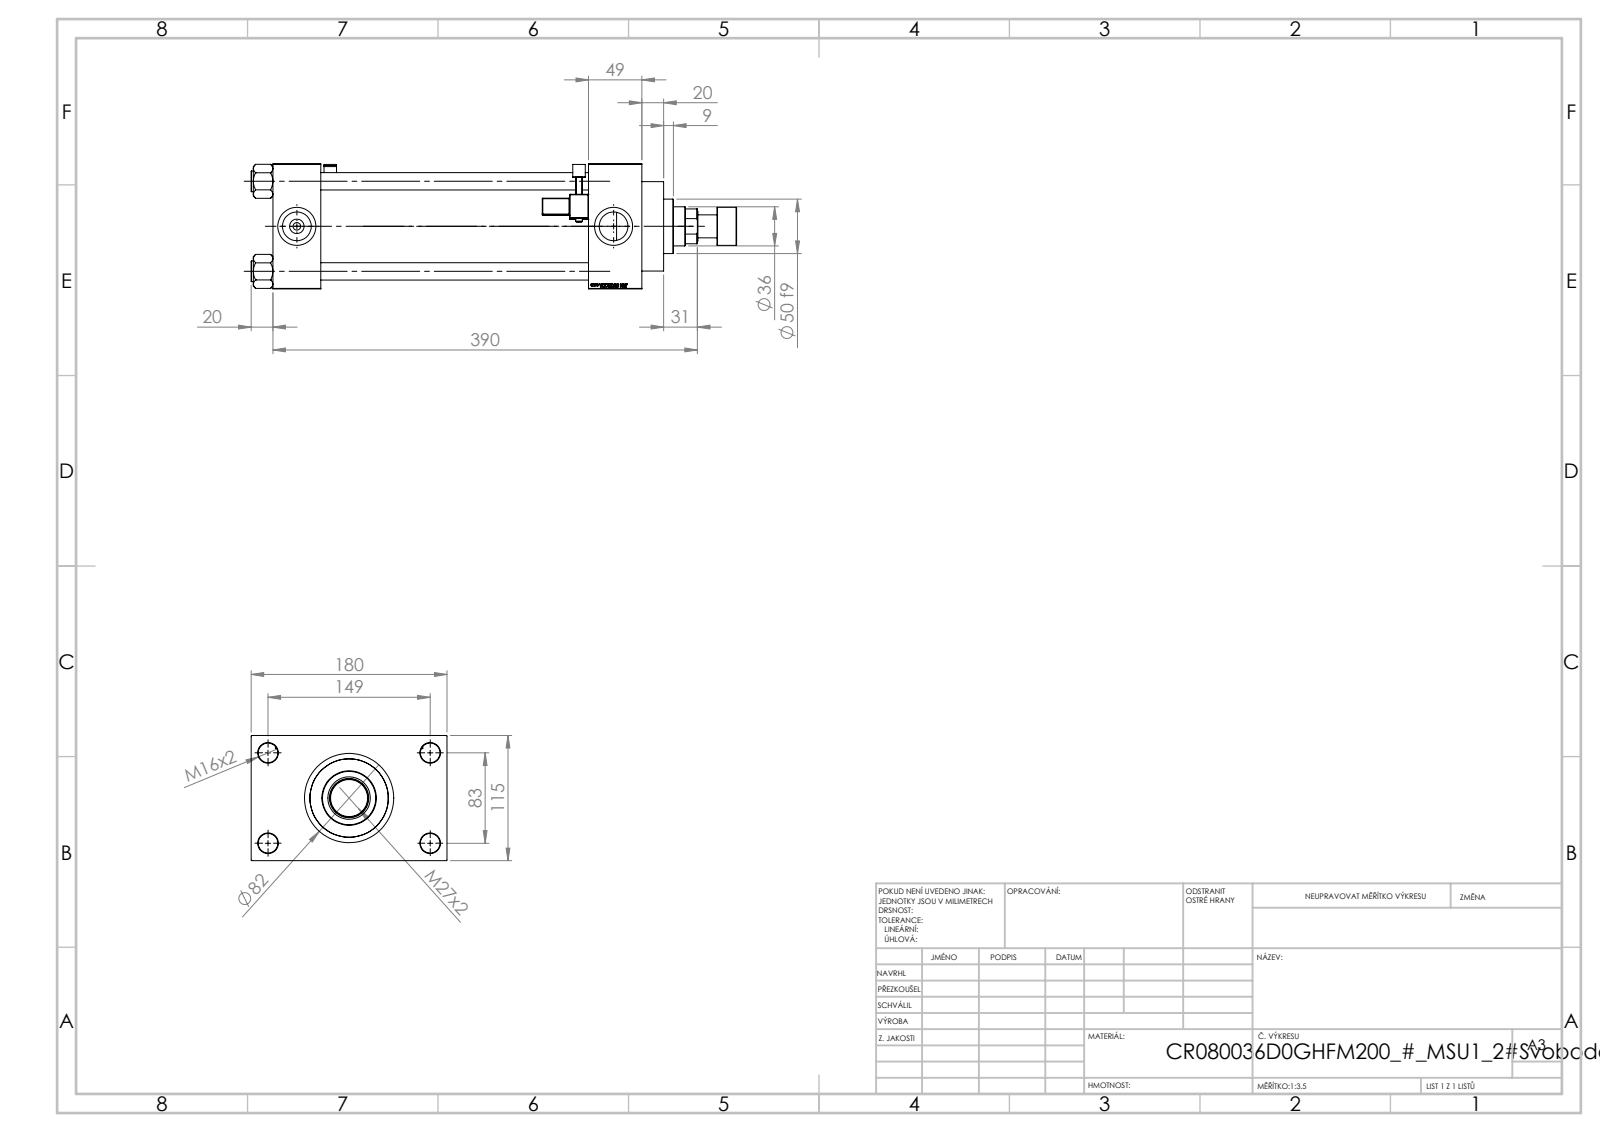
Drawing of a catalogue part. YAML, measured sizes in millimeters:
part_name: "V215CR_VCP_D; V215CR_D_TYCINKA; V215CR_ROD_END_F; V215_VC_A (+3 more)"
step_written_by: "SolidWorks 2019 (CONFIG_CONTROL_DESIGN)"
units: millimeters
bodies: {solids: 14, faces: 1319, planar: 607, cylindrical: 152, other: 560}
overall_size: [446, 180, 115]
volume: 2513000
surface_area: 465033
round_holes:
  - {diameter: 16, count: 4}
  - {diameter: 18, count: 4}
  - {diameter: 7, count: 2}
  - {diameter: 26.44, count: 2}
  - {diameter: 35, count: 2}
  - {diameter: 25.5, count: 1}
  - {diameter: 36, count: 1}
  - {diameter: 39, count: 1}
  - {diameter: 61, count: 1}
  - {diameter: 72, count: 1}
  - {diameter: 80, count: 1}
round_bosses_or_shafts:
  - {diameter: 19, count: 4}
  - {diameter: 6, count: 2}
  - {diameter: 86, count: 1}
  - {diameter: 82, count: 1}
  - {diameter: 50, count: 1}
  - {diameter: 35, count: 1}
  - {diameter: 21, count: 1}
partial_cylinders:
  - {radius: 0.5, count: 48}
  - {radius: 1, count: 2}
  - {radius: 2.5, count: 2}
  - {radius: 4, count: 2}
face_to_face_distances: [115, 246, 49, 295, 44, 290, 339, 32.5, 147.5, 180]
hole_center_spacings: [33.15, 58.48, 82.7, 85.28, 89.24, 115.85, 142.43, 83]
